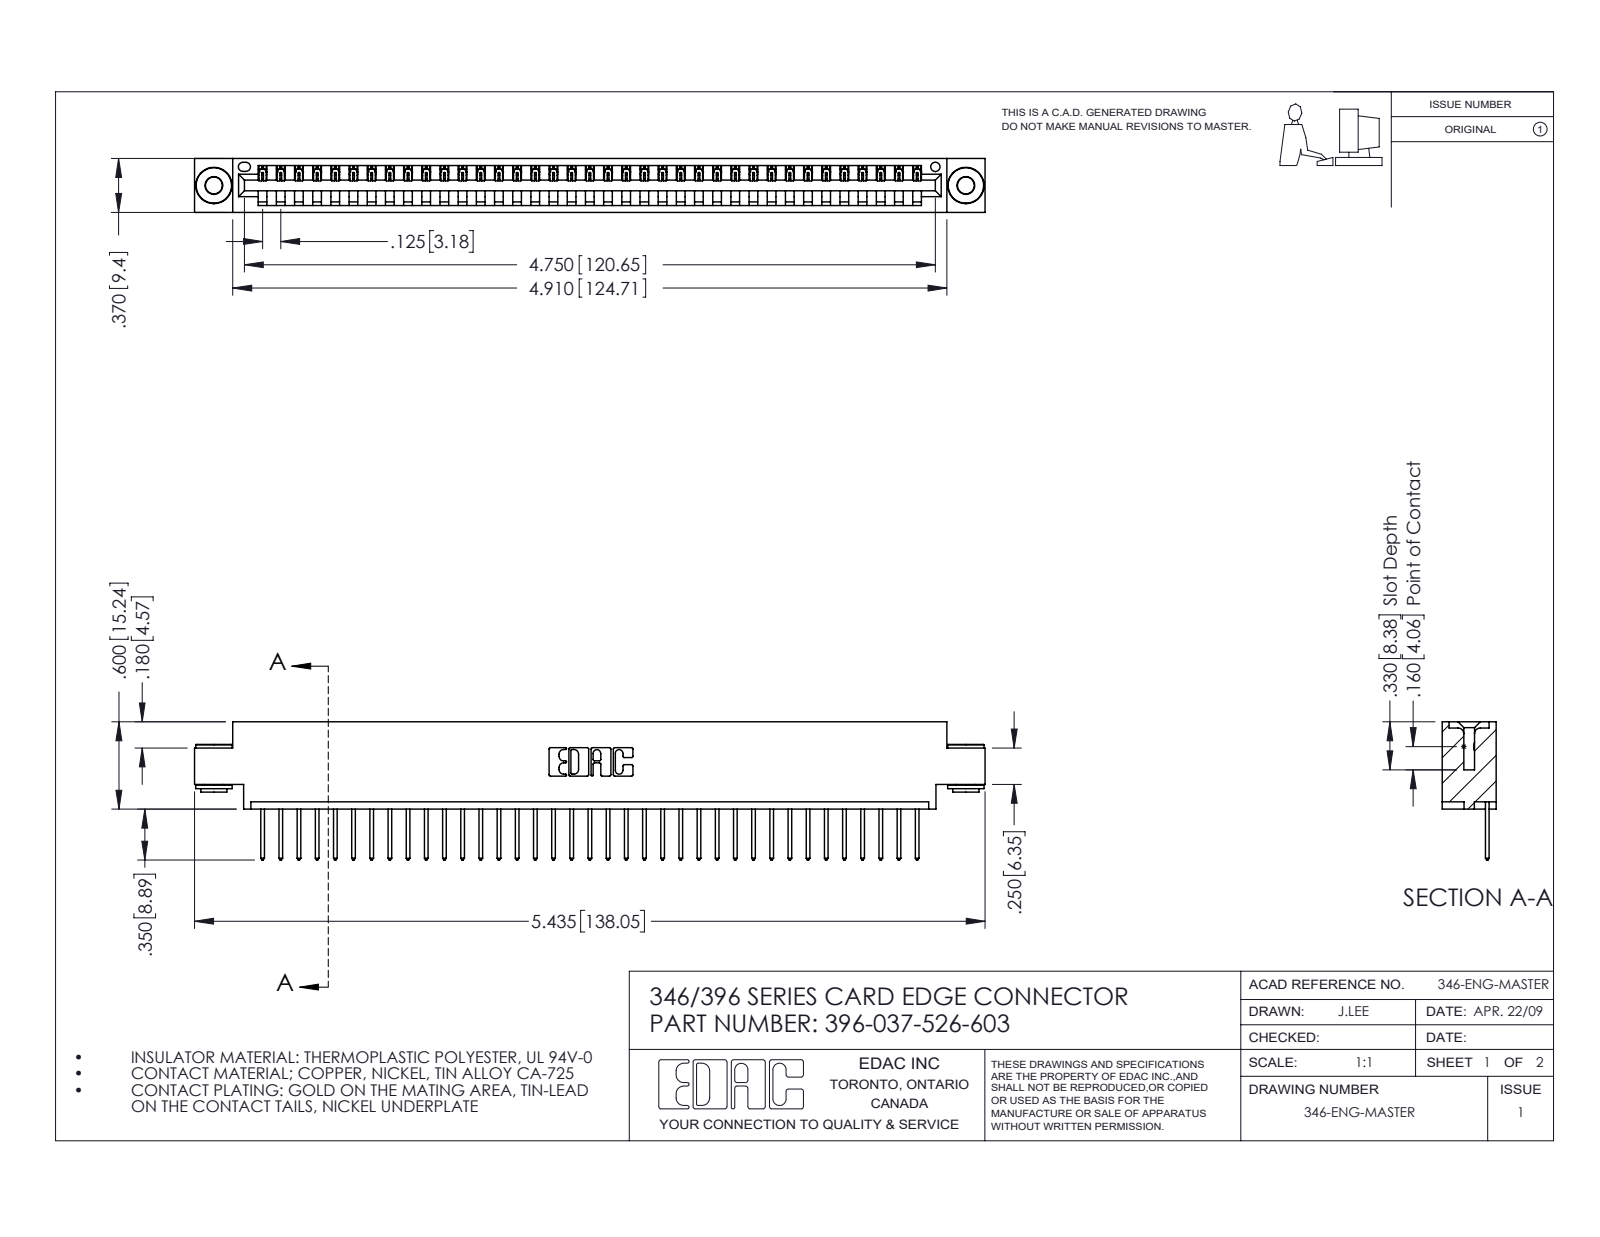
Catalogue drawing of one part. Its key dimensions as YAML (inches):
part_name: "346 Part_0.170 Offset - 0.156 Dia-TH; 345-250-002_345-250-002-102; 345-292-001_345-293-126; 396-037-526-603"
step_written_by: "SolidWorks 2016 (CONFIG_CONTROL_DESIGN)"
units: inches
bodies: {solids: 40, faces: 2310, planar: 1570, cylindrical: 732, other: 8}
overall_size: [5.435, 0.95, 0.37]
volume: 0.794
surface_area: 25.66
round_holes:
  - {diameter: 0.116, count: 2}
  - {diameter: 0.156, count: 2}
  - {diameter: 0.064, count: 1}
round_bosses_or_shafts:
  - {diameter: 0.25, count: 2}
  - {diameter: 0.18, count: 2}
  - {diameter: 0.136, count: 2}
partial_cylinders:
  - {radius: 0.006, count: 74}
  - {radius: 0.01, count: 74}
  - {radius: 0.01, count: 22}
  - {radius: 0.007, count: 6}
  - {radius: 0.031, count: 6}
  - {radius: 0.026, count: 3}
  - {radius: 0.031, count: 2}
  - {radius: 0.04, count: 2}
face_to_face_distances: [0.048, 0.322, 0.37, 0.25, 0.025, 0.072, 0.298, 0.148, 0.222, 0.1]
hole_center_spacings: [0.246, 4.961, 5.17]
